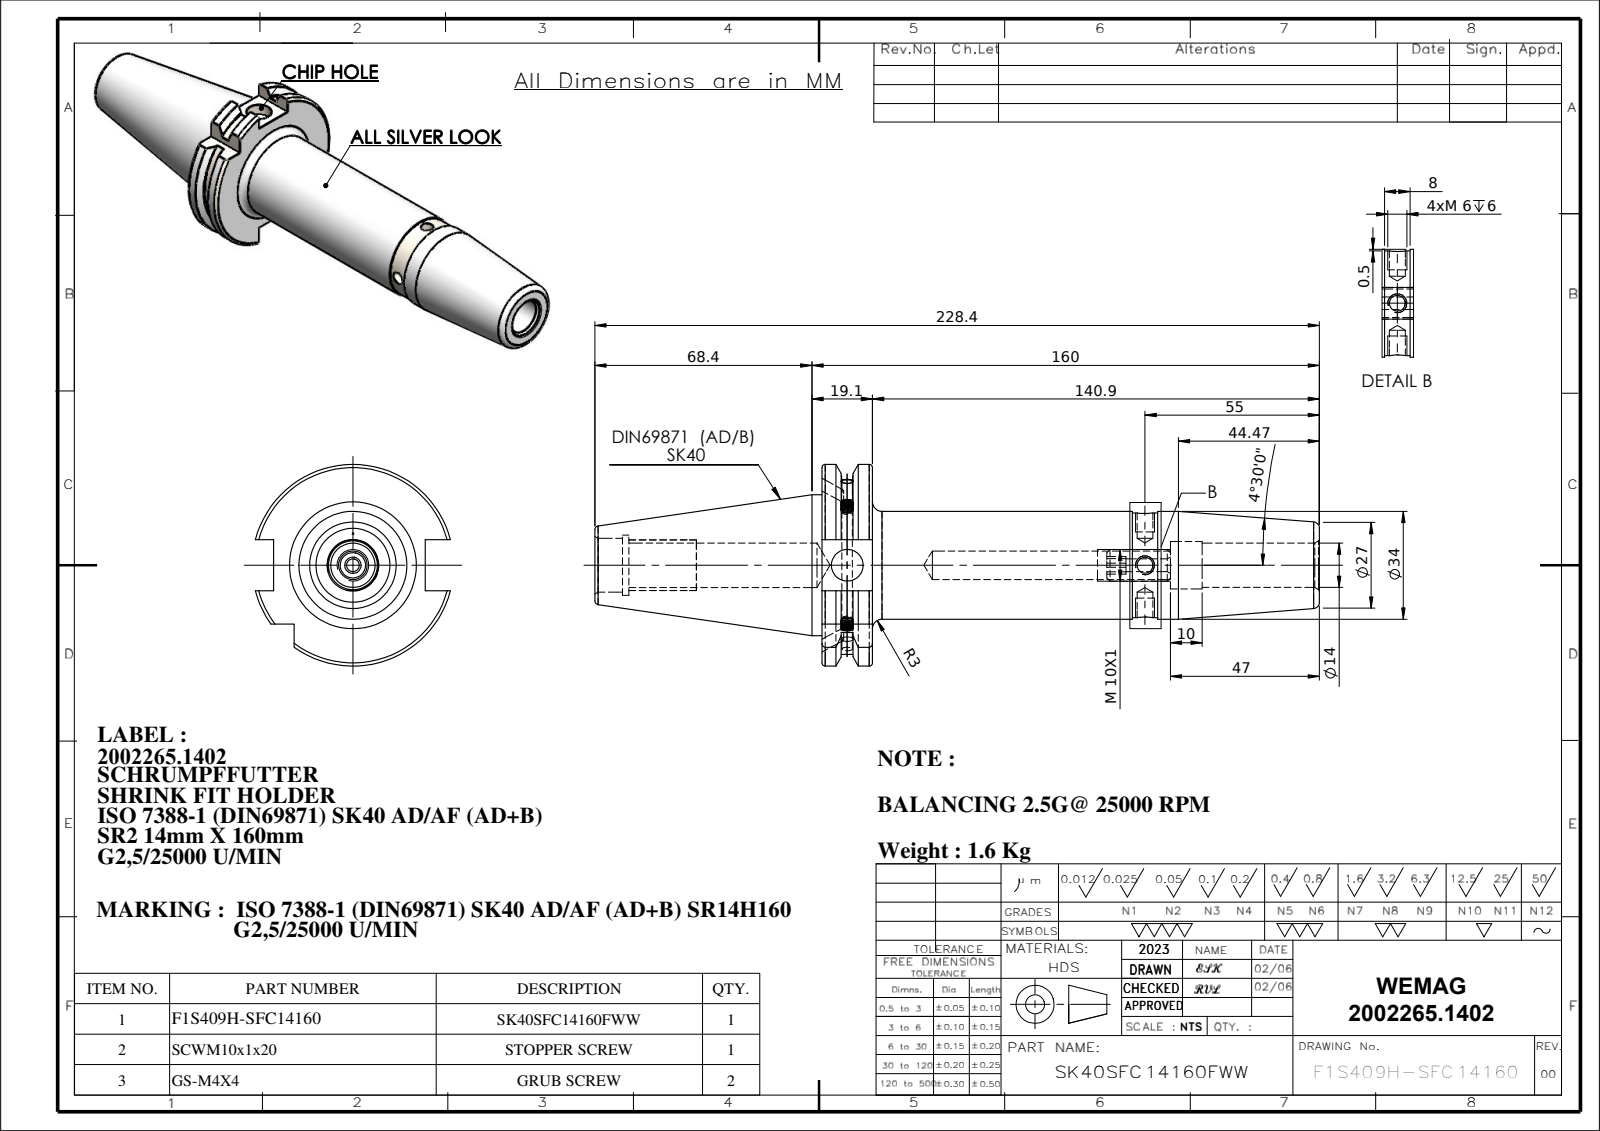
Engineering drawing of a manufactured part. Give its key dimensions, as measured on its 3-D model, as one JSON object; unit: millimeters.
{"part_name": "91406-SR214160; SCWM10X1; GS-M4X4_DIN 913 - M4 x 4-N; SK40SFC14160FWW", "step_written_by": "SolidWorks 2018 (CONFIG_CONTROL_DESIGN)", "units": "millimeters", "bodies": {"solids": 4, "faces": 237, "planar": 59, "cylindrical": 68, "other": 110}, "overall_size": [228.4, 63.55, 61.48], "volume_mm3": 208909, "surface_area_mm2": 41055, "round_holes": [[5, 2], [3.3, 1], [4, 1], [9, 1], [10, 1], [13.99, 1], [14, 1], [14.99, 1], [17, 1], [19, 1]], "round_bosses_or_shafts": [[4, 2], [44.45, 1], [34, 1], [33, 1], [10, 1]], "partial_cylinders_radius": [[28.12, 1], [31.77, 1]], "face_to_face_distances": [15.9, 156.8, 140.9, 16.1, 47.8, 109.8, 93.9, 47, 71.6, 87.5], "hole_center_spacings": [93.85]}
